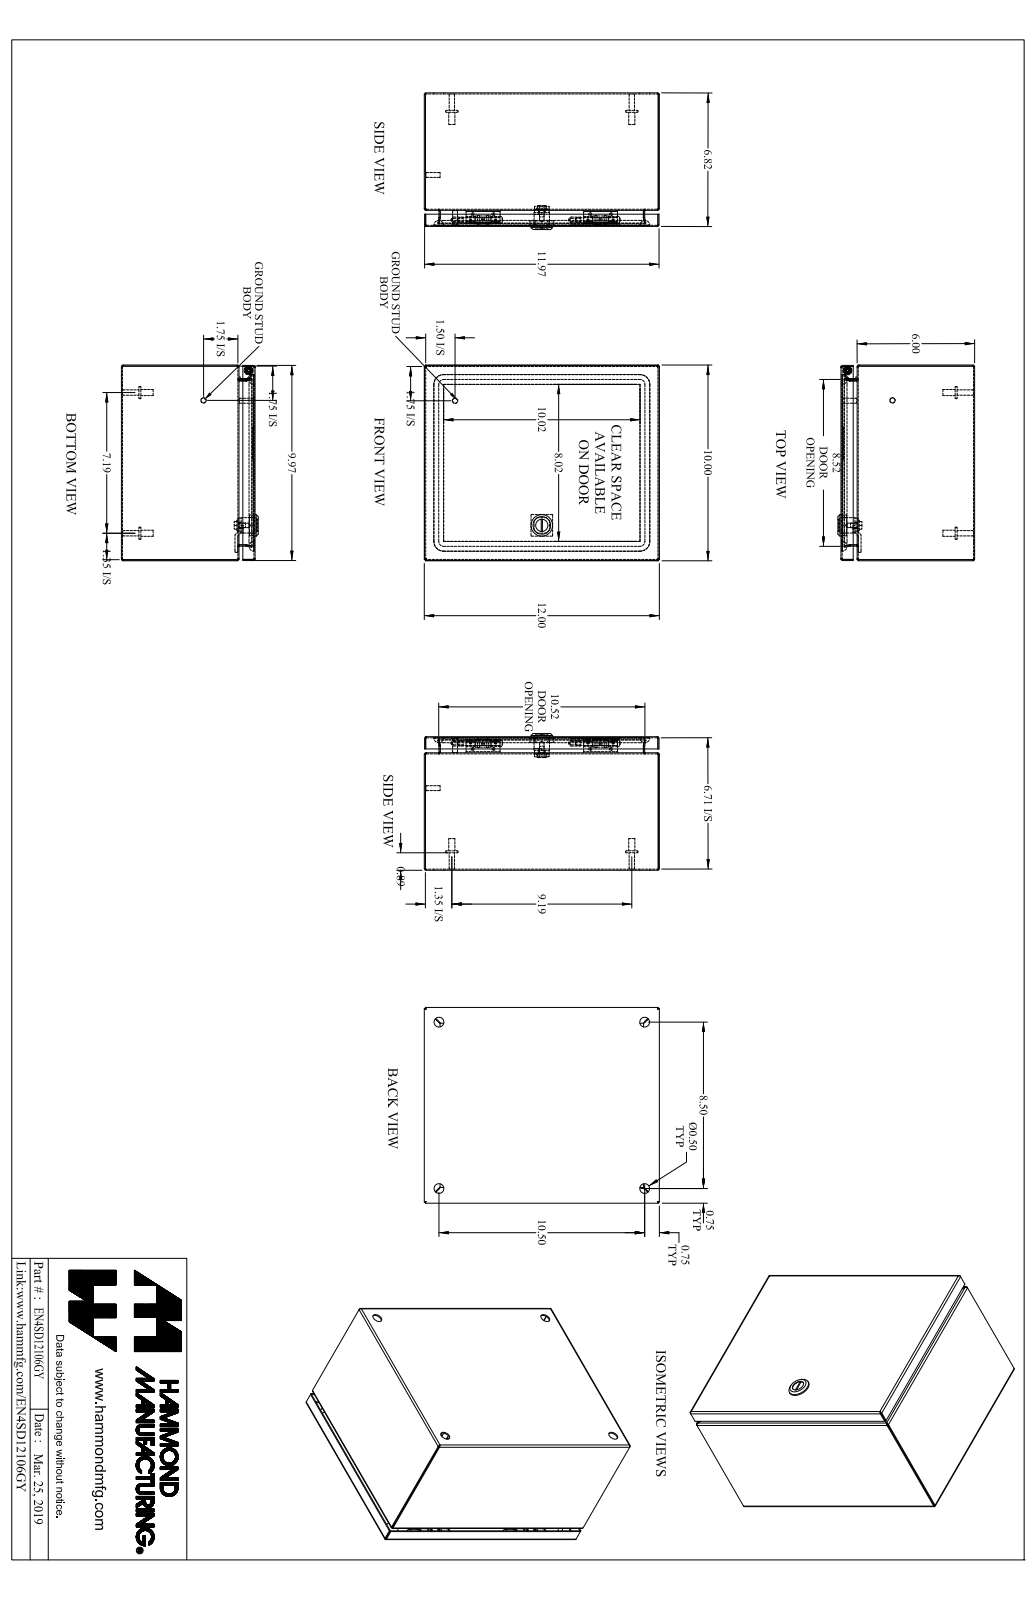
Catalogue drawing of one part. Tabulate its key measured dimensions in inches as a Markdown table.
| quantity | value |
| --- | --- |
| part name | EN4SD12106GY |
| STEP written by | SolidWorks 2019 (AUTOMOTIVE_DESIGN) |
| units | inches |
| bodies | 21 solids, 541 faces (285 planar, 162 cylindrical, 94 other) |
| overall size | 12 × 10 × 6.982 |
| volume | 38.28 in³ |
| surface area | 1 281 in² |
| round holes (diameter × count) | 0.5 × 4, 0.172 × 1, 0.232 × 1, 0.24 × 1, 0.242 × 1, 0.625 × 1, 0.785 × 1 |
| round bosses / shafts (diameter × count) | 0.625 × 4, 0.313 × 4, 0.27 × 4, 0.281 × 2, 0.25 × 2, 1.1 × 1, 0.525 × 1, 0.455 × 1 |
| partial cylindrical surfaces (radius × count) | 0.029 × 21, 0.086 × 21, 0.25 × 16, 19 × 8, 0.006 × 4, 0.062 × 4, 0.499 × 4, 0.125 × 2 |
| main face-to-face distances | 0.057, 6.765, 9.943, 6.708, 6.822, 11.943, 9.886, 10, 11.886, 12 |
| hole center spacings | 8.5, 10.5, 13.509, 5.356, 5.356, 9.106, 9.107 |
